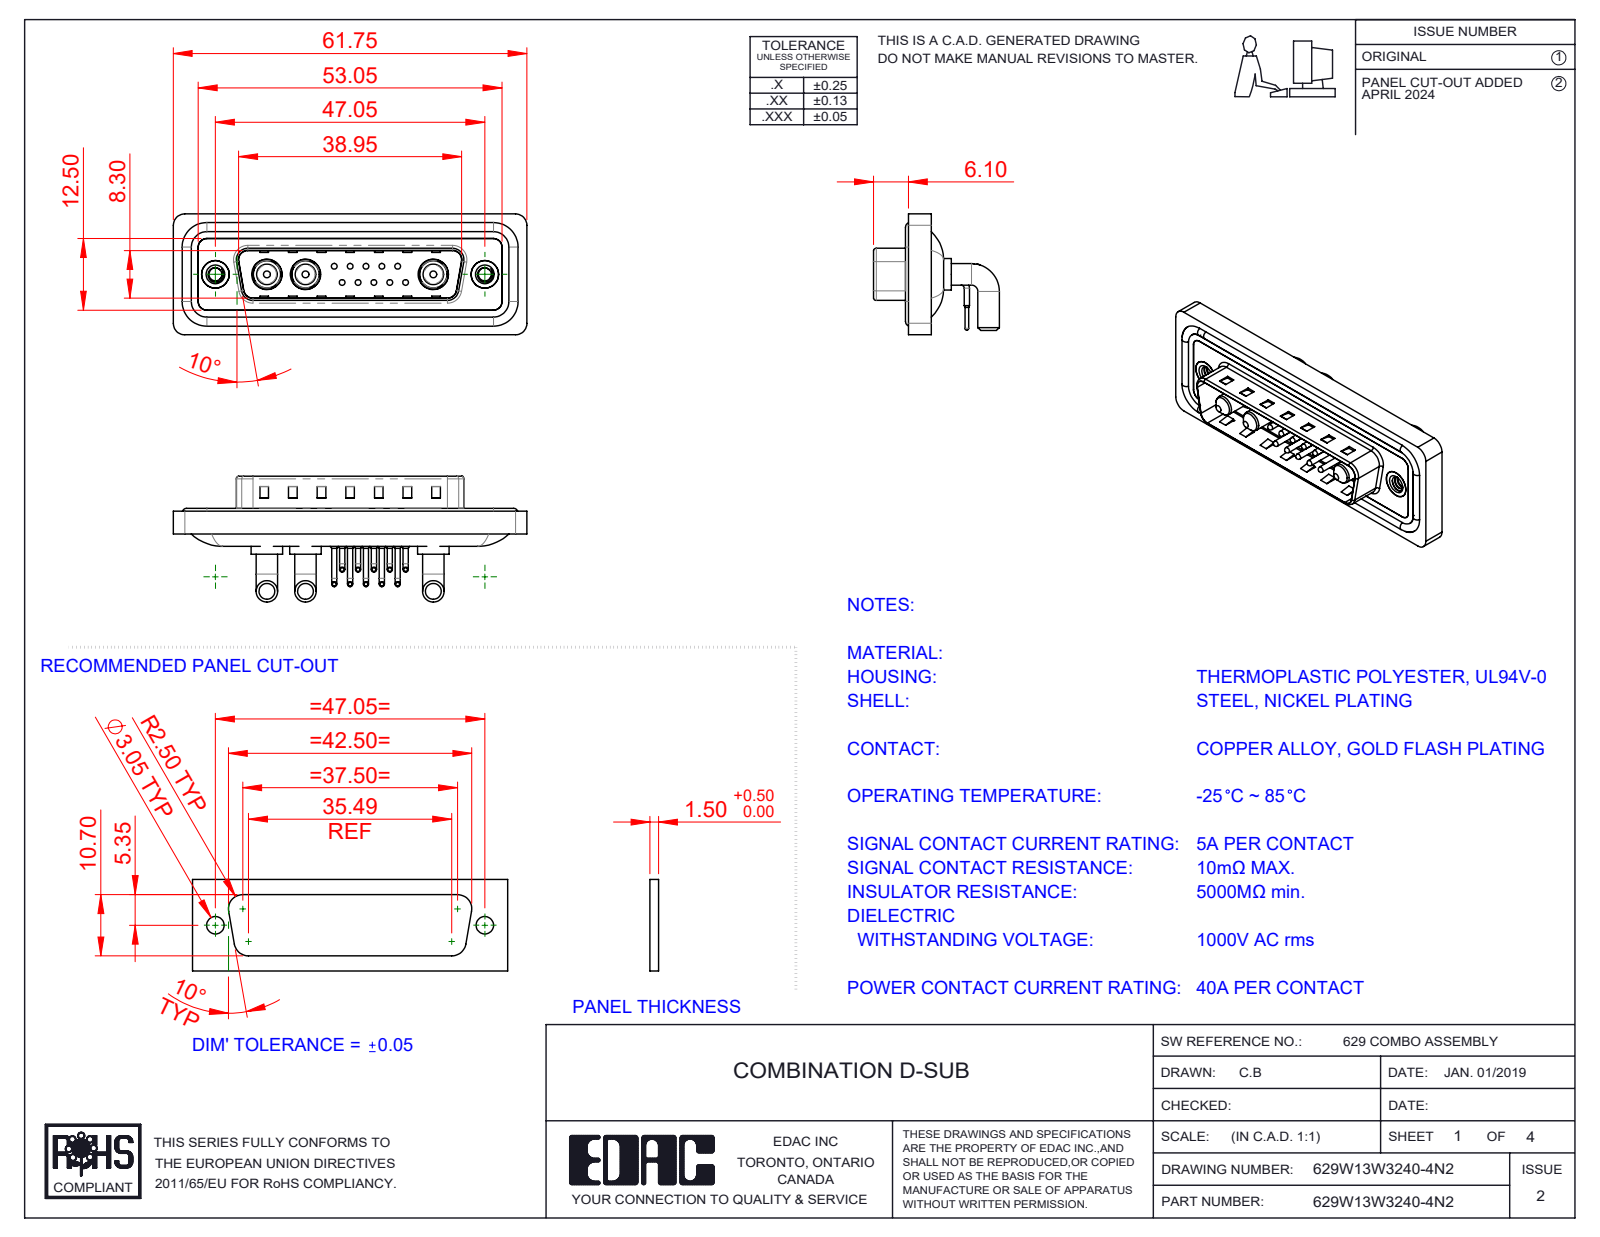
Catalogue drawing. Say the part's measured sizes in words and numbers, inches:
The part is named "629Combo Housing_13W3; 629Combo Contact Row 2; 629Combo Waterproof Housing_25 Contacts; 629Combo Contact Row 1 (+5 more)". Its 3-D file was written by "SolidWorks 2023 (CONFIG_CONTROL_DESIGN)". It is 23 solids with 1712 faces: 879 planar, 611 cylindrical and 222 other. Overall it measures 2.431 by 0.865 by 0.831 inches. Its volume is 0.478 cubic inches and its surface area 19.57 square inches. Round holes: 10 of diameter 0.03, 10 of diameter 0.063, 10 of diameter 0.079, 3 of diameter 0.191, 3 of diameter 0.209, 2 of diameter 0.089, 2 of diameter 0.157, 2 of diameter 0.189, 2 of diameter 0.197. Round bosses or shafts: 20 of diameter 0.035, 10 of diameter 0.059, 10 of diameter 0.039, 10 of diameter 0.026, 6 of diameter 0.148, 4 of diameter 0.063, 3 of diameter 0.217, 3 of diameter 0.205. Partial cylindrical surfaces (rounded edges, fillets, slot ends): 18 of radius 0.059, 18 of radius 0.079, 10 of radius 0.04, 8 of radius 0.02, 8 of radius 0.063, 4 of radius 0.01, 4 of radius 0.024, 4 of radius 0.026. The main face-to-face distances are 0.016, 0.114, 0.031, 0.161, 0.043, 0.083, 0.063, 0.177, 0.098, 0.059. The hole center spacings are 0.124, 0.109, 0.198, 0.218, 0.295, 0.198, 0.327, 0.398.
